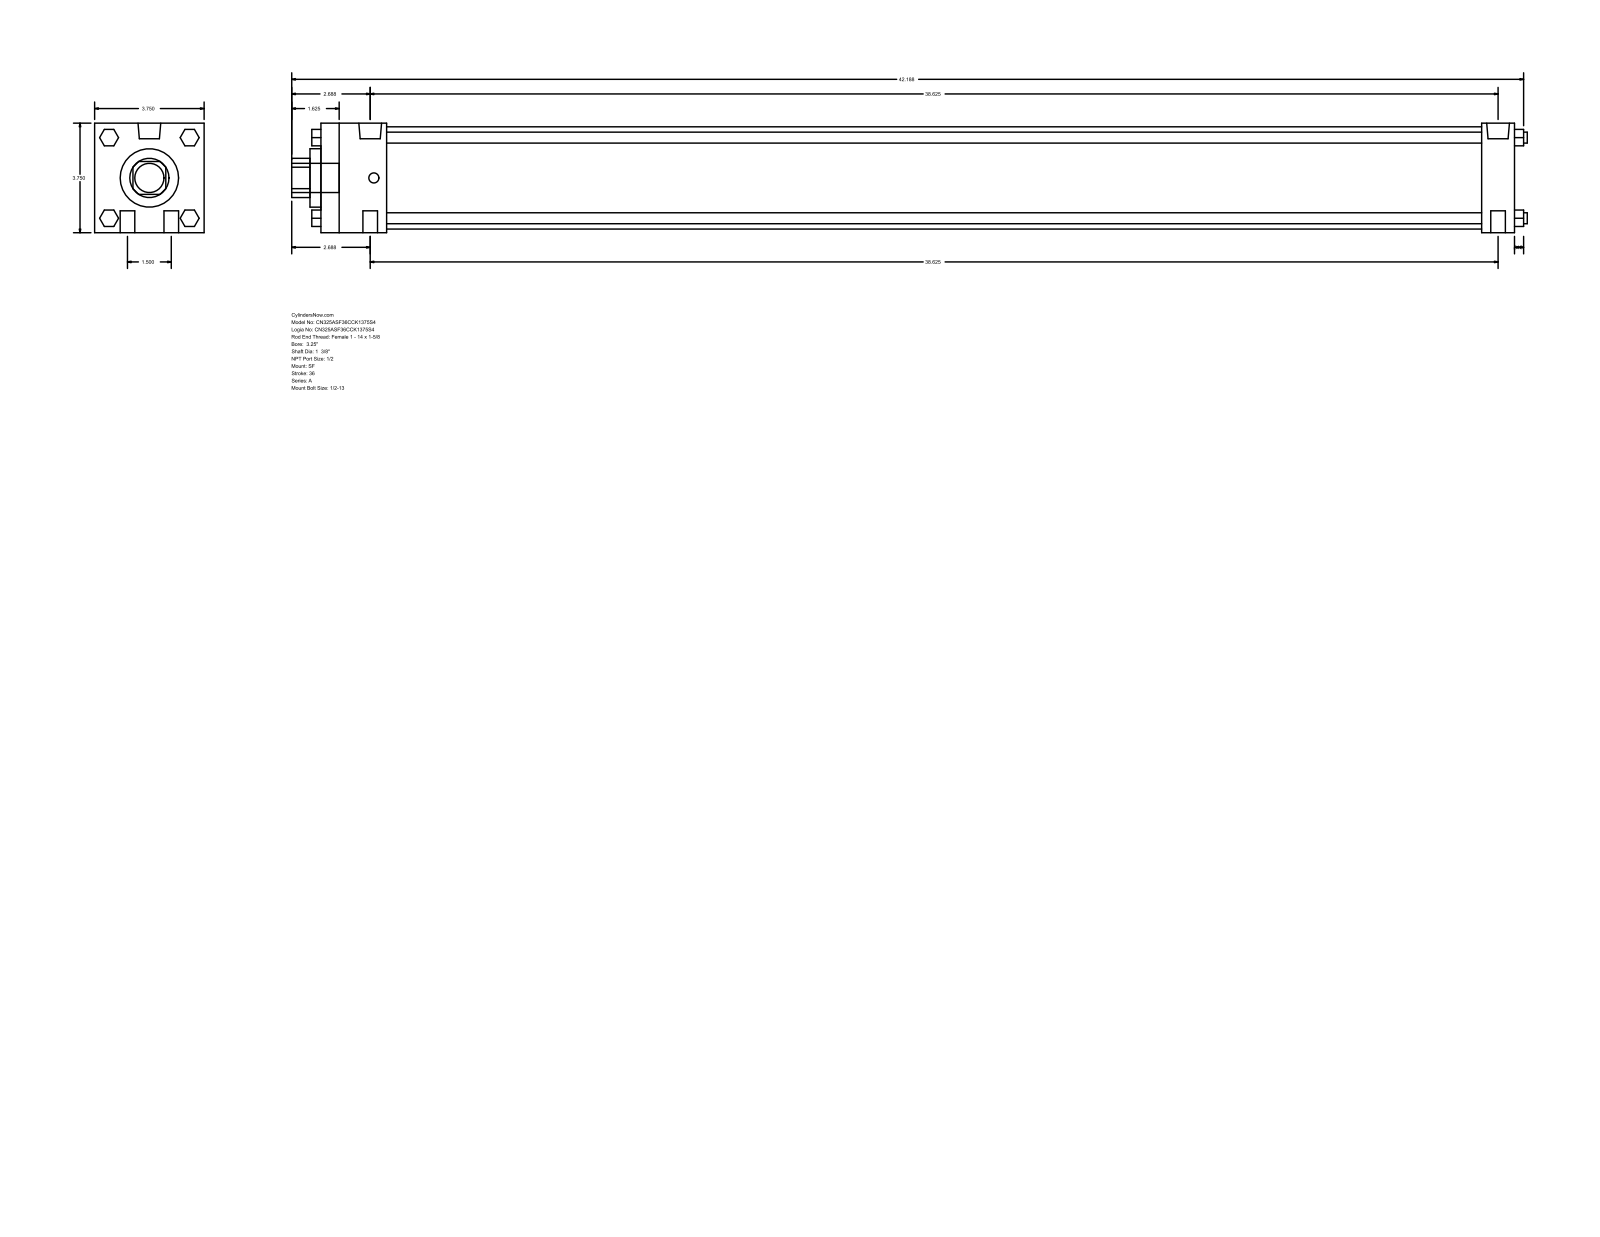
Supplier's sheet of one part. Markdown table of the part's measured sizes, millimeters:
| quantity | value |
| --- | --- |
| part name | A_SF__0325_1.375 |
| STEP written by | GSSL Pune (CONFIG_CONTROL_DESIGN) |
| units | millimeters |
| bodies | 0 solids, 124 faces (94 planar, 30 cylindrical, 0 other) |
| overall size | 1074.74 × 95.25 × 95.25 |
| round holes (diameter × count) | 34.92 × 1, 50.8 × 1, 88.9 × 1 |
| round bosses / shafts (diameter × count) | 12.7 × 4, 9.53 × 4, 19.77 × 2, 8.73 × 2, 25.4 × 1 |
| partial cylindrical surfaces (radius × count) | 17.06 × 1 |
| main face-to-face distances | 95.24, 1038.22, 28.57, 1009.65, 57.15, 952.5, 981.07, 9.52, 66.67, 1019.17 |
